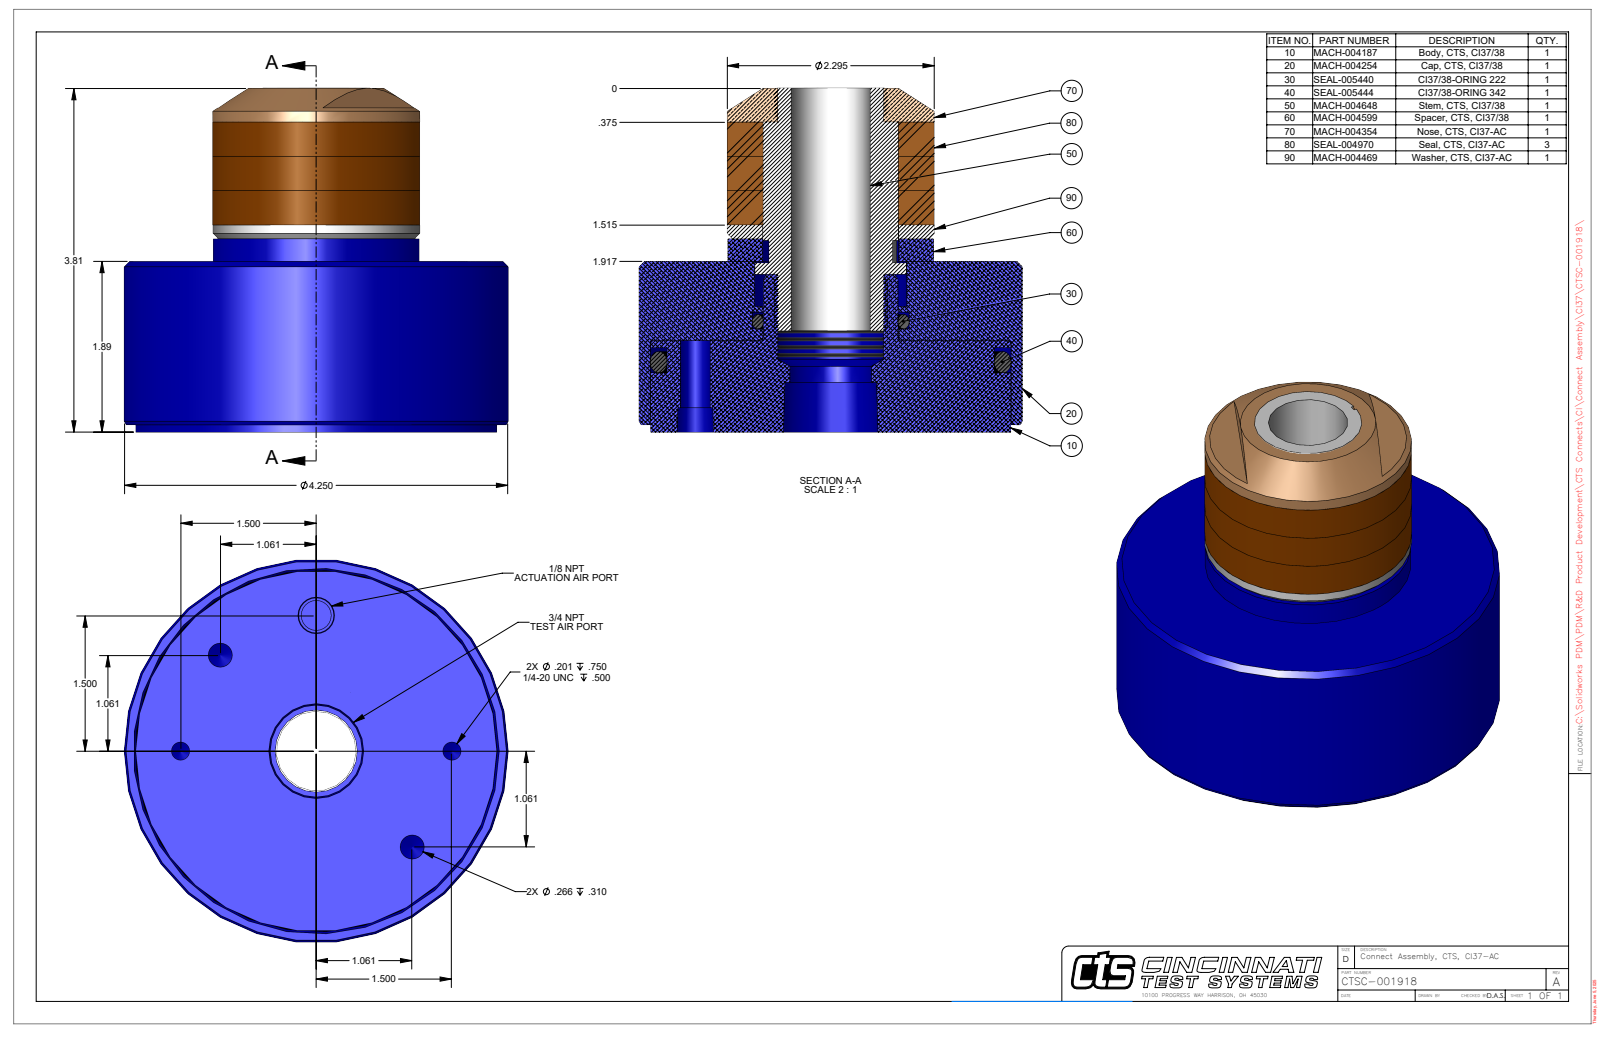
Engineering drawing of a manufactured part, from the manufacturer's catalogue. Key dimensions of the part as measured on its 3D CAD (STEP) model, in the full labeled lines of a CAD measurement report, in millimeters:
Part name (STEP PRODUCT): CTSC-001918
STEP written by: SolidWorks 2023 (AUTOMOTIVE_DESIGN)
Units: millimetres
Bodies: 1 solid, 82 faces (28 planar, 31 cylindrical, 23 other)
Overall size (bounding box): 108 × 108 × 96.9
Volume: 517 500 mm³ · Surface area: 60 800 mm²
Round holes (diameter × count): ⌀5.1 ×2, ⌀6.8 ×2, ⌀8.4 ×1, ⌀22.4 ×1, ⌀38.4 ×1, ⌀42.9 ×1, ⌀101.6 ×1
Round bosses / shafts (diameter × count): ⌀108 ×1, ⌀101.4 ×1, ⌀58.3 ×1, ⌀57.9 ×1, ⌀42.5 ×1, ⌀38.1 ×1
Partial cylindrical surfaces — rounded edges, fillets, slot ends (radius × count): R14.9 ×1
Main face-to-face distances: 48.1, 2.1, 46, 91.2, 89.1, 43.1, 48.7, 96.8, 94.7, 5.6
Hole centre spacings: 38.1, 29.2, 70.4, 53.9, 76.2
